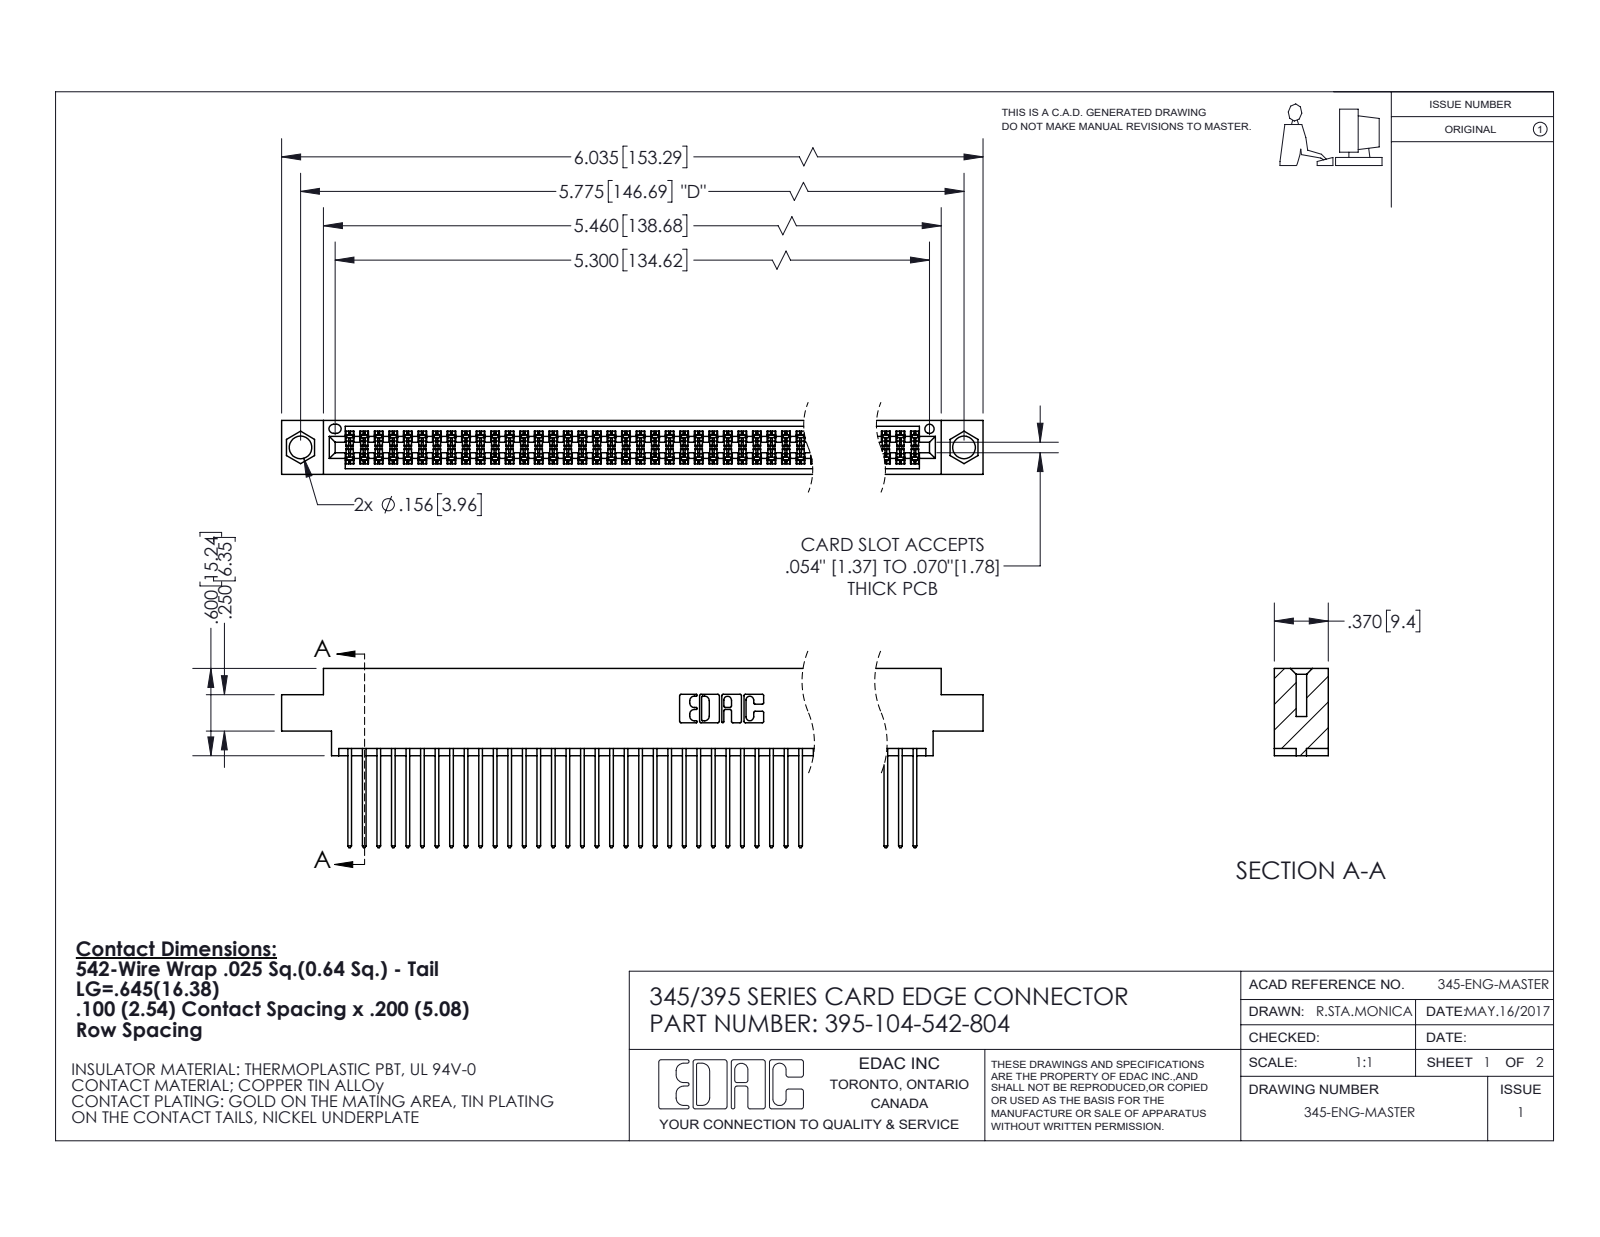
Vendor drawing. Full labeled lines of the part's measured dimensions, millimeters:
Part name (STEP PRODUCT): 345 Part_0.170 Offset - 0.156 Dia-TI; 345-292-001_345-293-142; 395-104-542-804
STEP written by: SolidWorks 2020 (CONFIG_CONTROL_DESIGN)
Units: millimetres
Bodies: 105 solids, 5344 faces (3530 planar, 1814 cylindrical, 0 other)
Overall size (bounding box): 153.3 × 31.3 × 9.4
Volume: 15 300 mm³ · Surface area: 24 990 mm²
Round holes (diameter × count): ⌀4 ×2, ⌀1.6 ×1
Partial cylindrical surfaces — rounded edges, fillets, slot ends (radius × count): R0.2 ×156, R0.3 ×104, R0.3 ×22, R0.2 ×6, R0.8 ×6, R0.7 ×3, R0.4 ×2, R0.5 ×2
Main face-to-face distances: 1.8, 7.6, 5.1, 2.5, 6.9, 0.6, 9.4, 5.7, 4.4, 3.8
Hole centre spacings: 6.9, 140.7, 146.7
